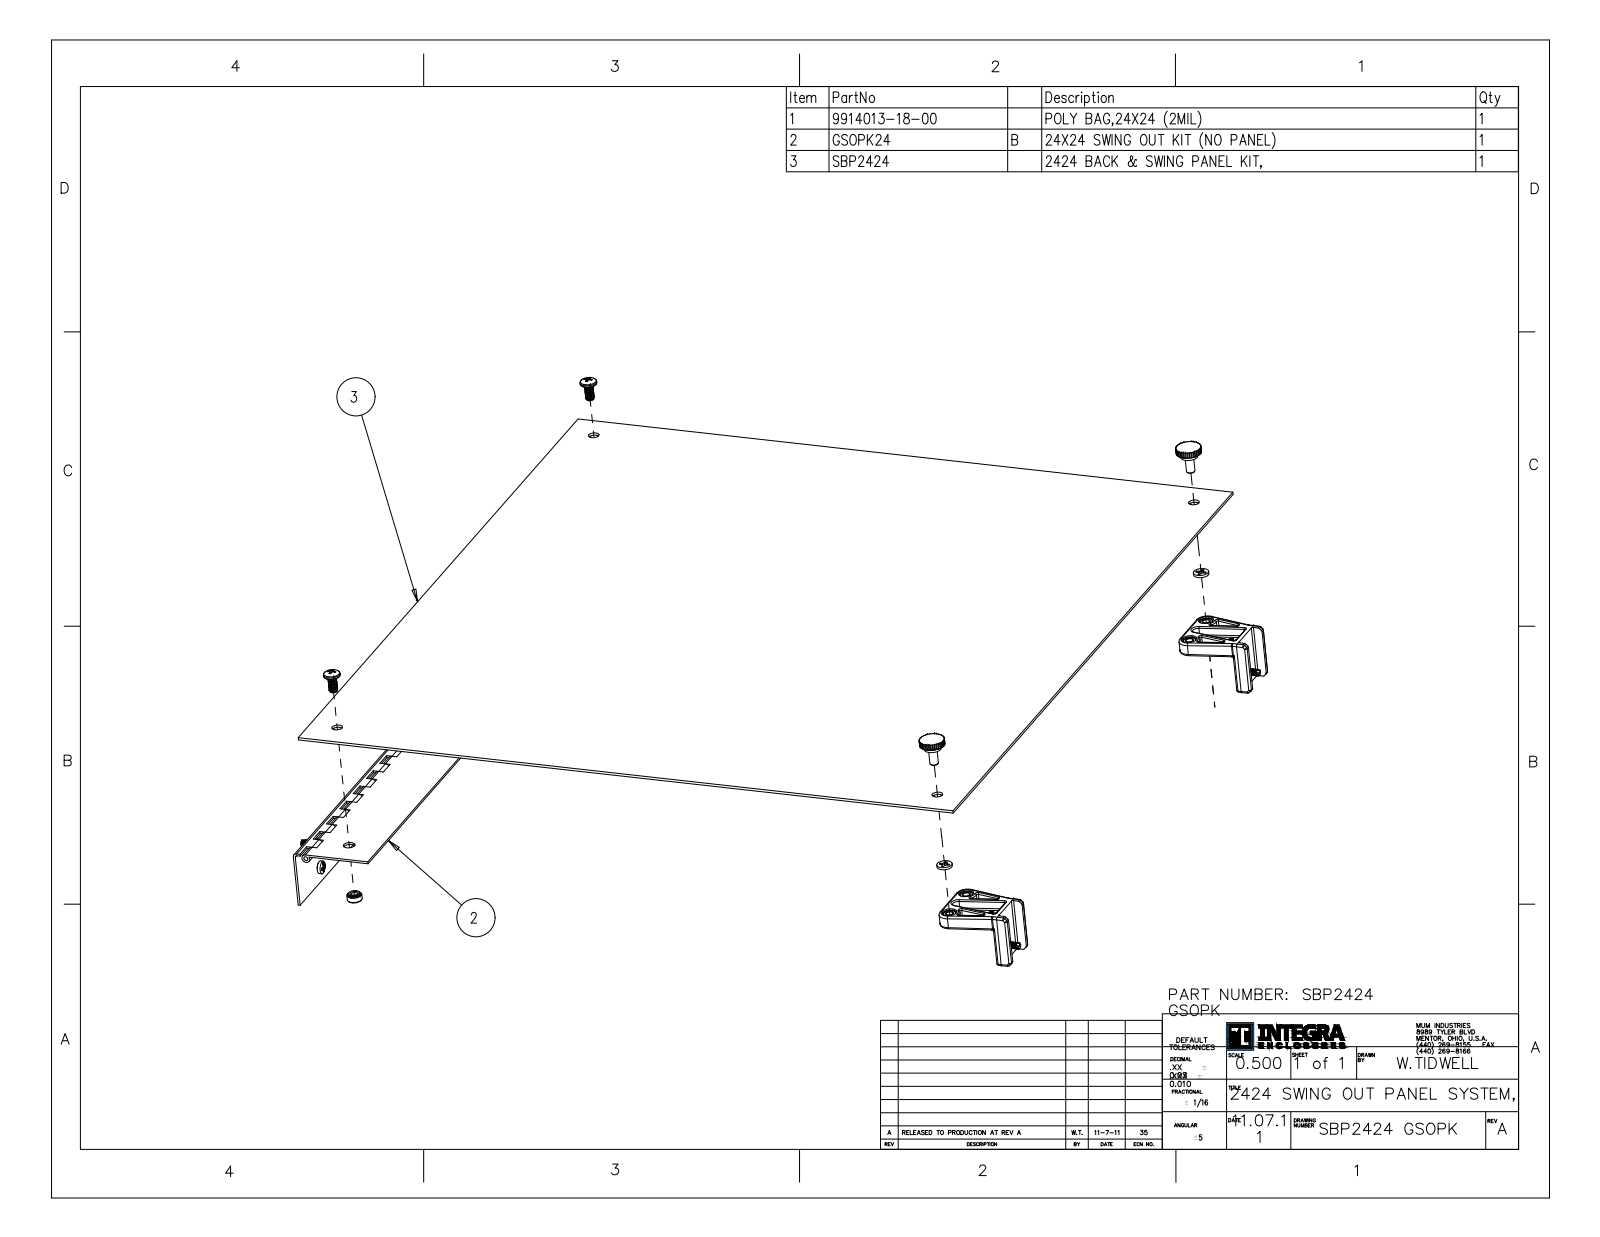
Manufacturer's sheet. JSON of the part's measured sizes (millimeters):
{"part_name": "SBP-2424GSOPK-P10", "step_written_by": "SolidWorks 2017 (AUTOMOTIVE_DESIGN)", "units": "millimeters", "bodies": {"solids": 27, "faces": 3050, "planar": 1870, "cylindrical": 630, "other": 550}, "overall_size": [586.2, 533.4, 54.2], "volume_mm3": 683500, "surface_area_mm2": 728400, "round_holes": [[5.4, 8], [6.4, 6], [7.9, 6], [5.2, 4], [11.3, 4], [5.2, 2], [6.8, 2], [7.9, 2], [8, 2], [3.2, 1], [3.2, 1]], "round_bosses_or_shafts": [[9.5, 10], [4.8, 6], [4.1, 6], [6.4, 5], [12.5, 4], [8.9, 4], [4.7, 4], [12.9, 2]], "partial_cylinders_radius": [[0.3, 180], [1.5, 53], [1, 34], [1.3, 4], [2.7, 4], [3.2, 4], [7.9, 4], [2.2, 2]], "face_to_face_distances": [1.9, 1.6, 3.5, 533.4, 16.5, 549.9, 4.1, 566.4, 564.8, 562.4], "hole_center_spacings": [489, 691.5, 31.8, 457.2, 489, 0.5, 457.2, 479.5]}
